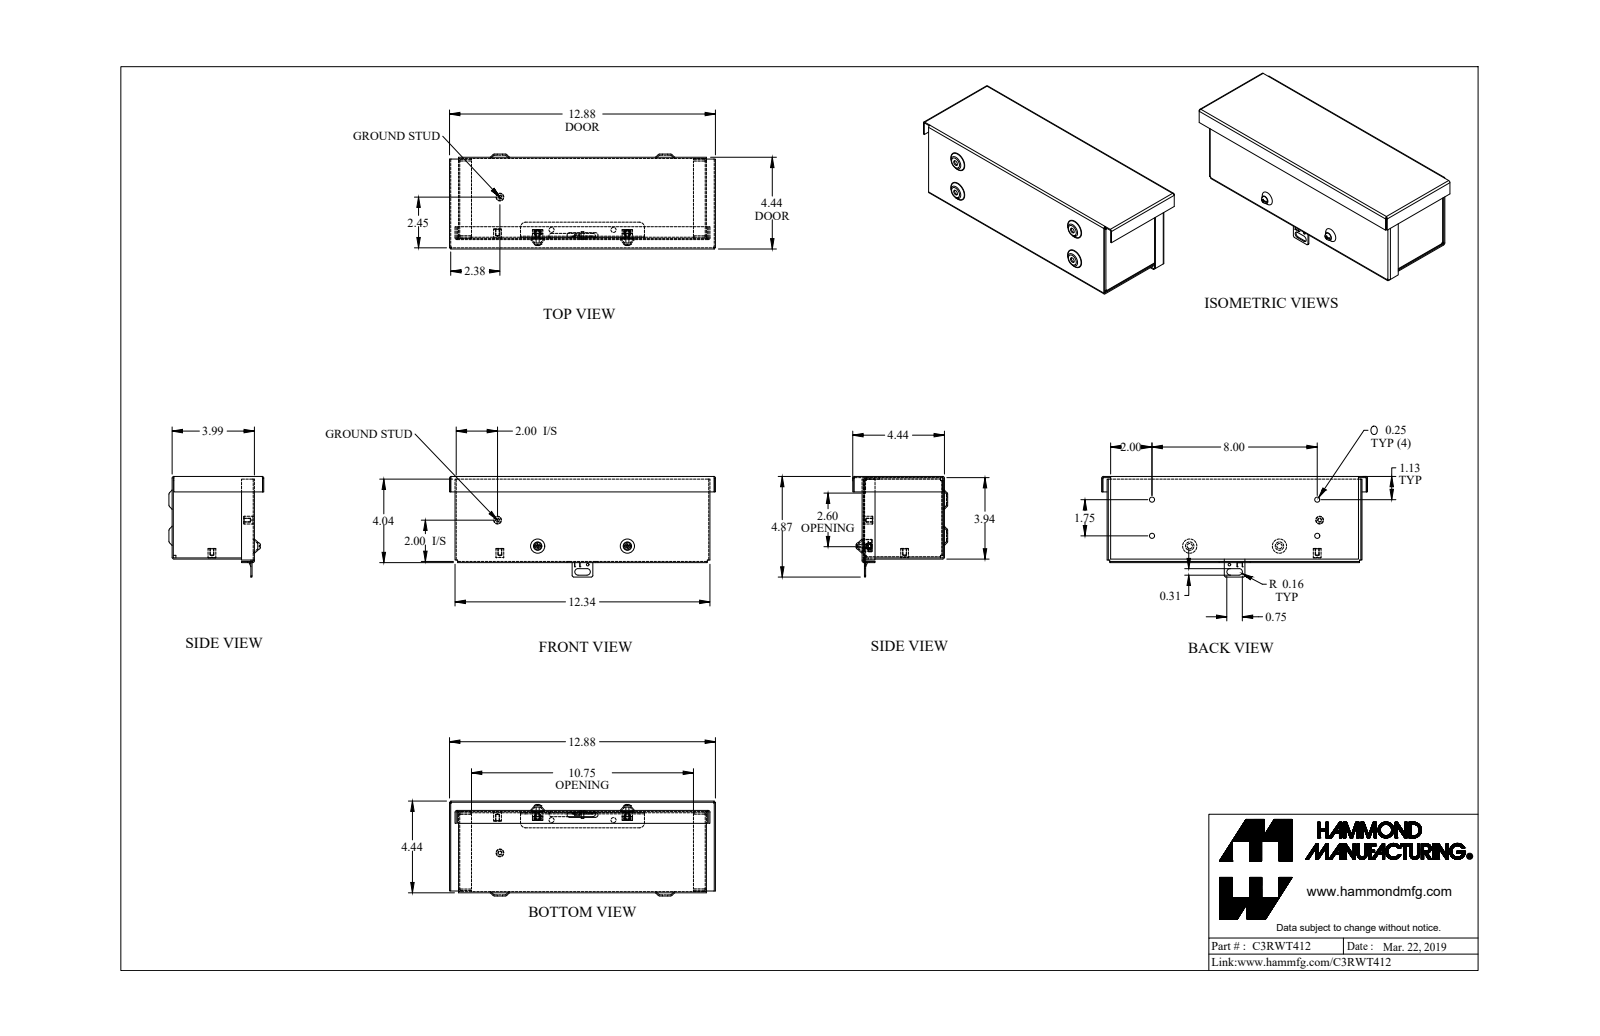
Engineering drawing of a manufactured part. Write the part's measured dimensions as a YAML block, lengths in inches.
part_name: "C3RWT412_Default"
step_written_by: "SolidWorks 2019 (CONFIG_CONTROL_DESIGN)"
units: inches
bodies: {solids: 19, faces: 645, planar: 344, cylindrical: 201, other: 100}
overall_size: [13.5, 4.871, 4.594]
volume: 17.03
surface_area: 602.8
round_holes:
  - {diameter: 0.25, count: 6}
  - {diameter: 0.156, count: 4}
  - {diameter: 0.203, count: 2}
  - {diameter: 0.214, count: 2}
  - {diameter: 0.23, count: 2}
  - {diameter: 0.125, count: 1}
  - {diameter: 0.137, count: 1}
  - {diameter: 0.2, count: 1}
  - {diameter: 0.215, count: 1}
round_bosses_or_shafts:
  - {diameter: 0.19, count: 3}
  - {diameter: 0.375, count: 2}
  - {diameter: 0.148, count: 2}
  - {diameter: 0.5, count: 1}
  - {diameter: 0.367, count: 1}
  - {diameter: 0.21, count: 1}
  - {diameter: 0.152, count: 1}
  - {diameter: 0.125, count: 1}
partial_cylinders:
  - {radius: 0.029, count: 18}
  - {radius: 0.086, count: 18}
  - {radius: 0.125, count: 12}
  - {radius: 0.08, count: 8}
  - {radius: 0.108, count: 8}
  - {radius: 0.25, count: 6}
  - {radius: 0.016, count: 4}
  - {radius: 0.022, count: 4}
face_to_face_distances: [0.057, 3.943, 3.928, 3.871, 3.886, 4, 3.985, 11.943, 0.172, 0.114]
hole_center_spacings: [2.179, 2.678, 2.899, 4.344, 4.571, 6.192, 6.569, 8.811]
